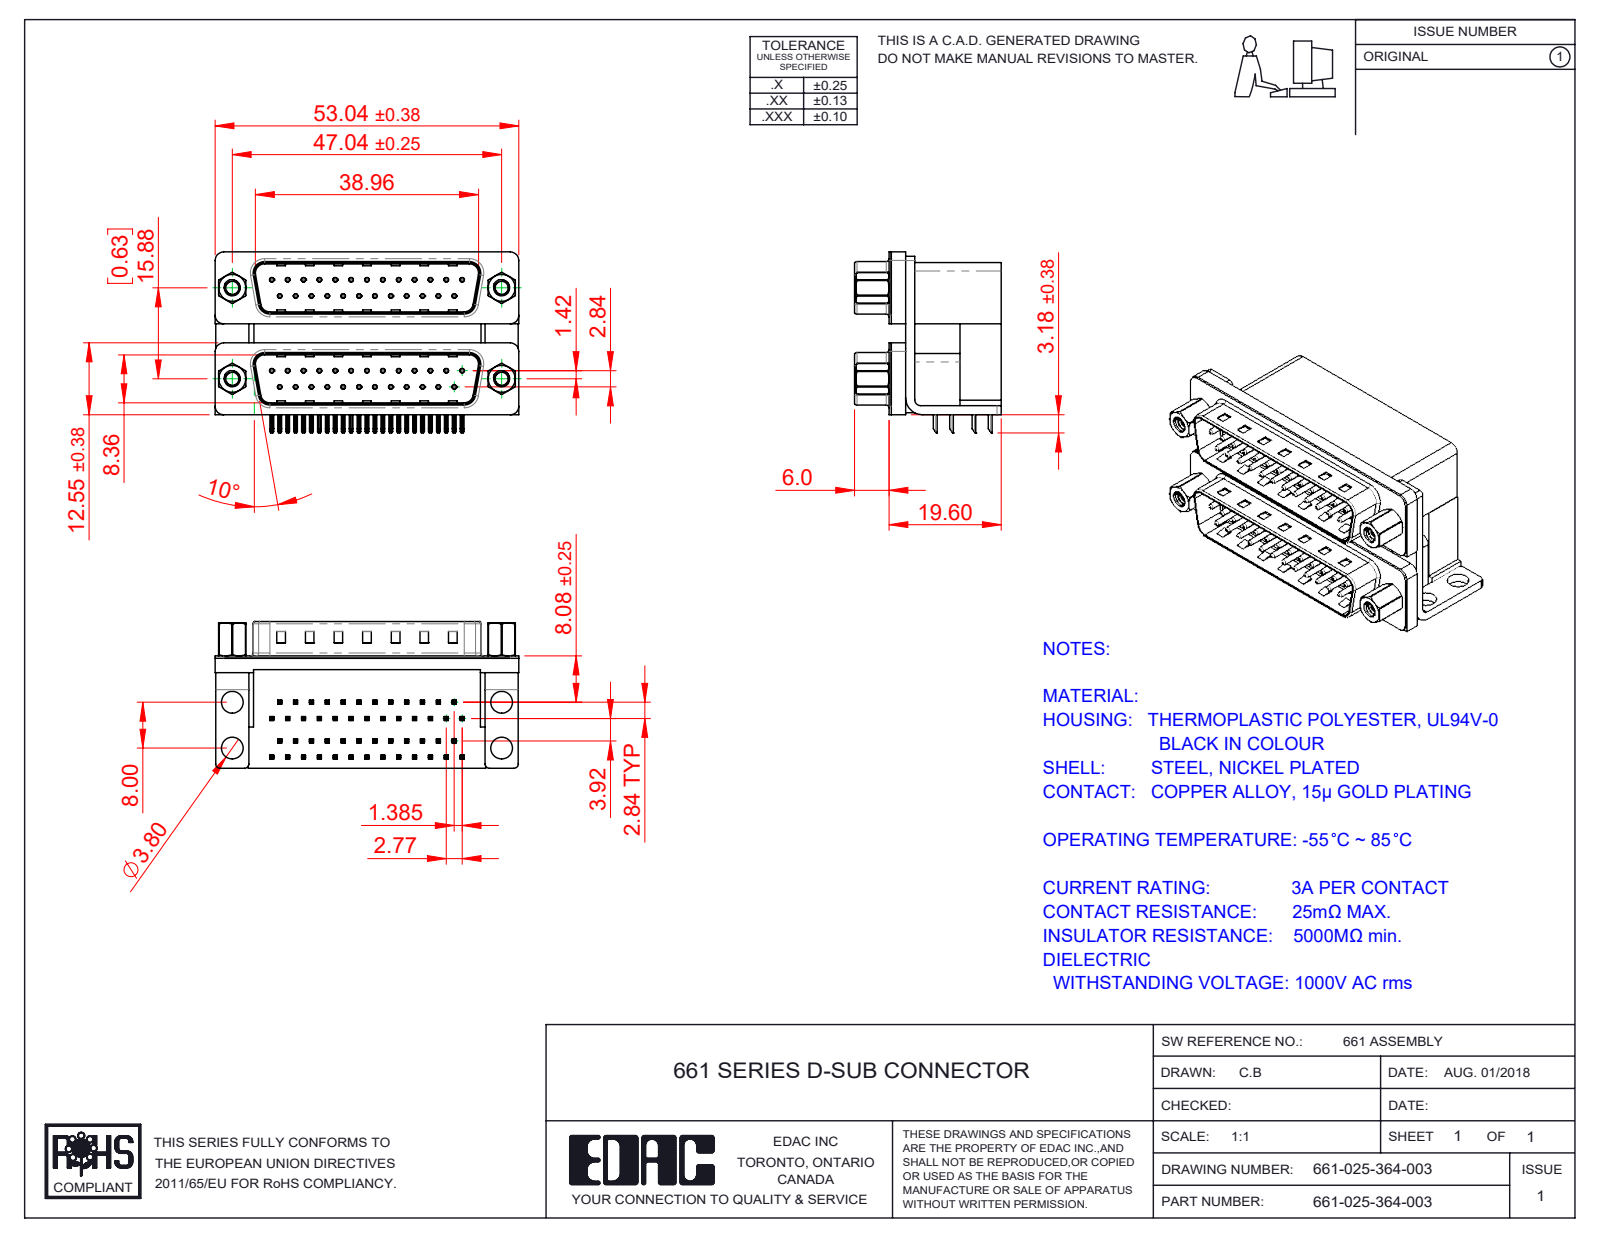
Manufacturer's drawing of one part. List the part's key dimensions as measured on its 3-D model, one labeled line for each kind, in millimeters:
Part name (STEP PRODUCT): 661 Contact Top Upper_L; 661 Contact Bottom Lower; 661 Shell_25 Contacts; 661 Housing Spacer_25 Contacts L (+8 more)
STEP written by: SolidWorks 2020 (CONFIG_CONTROL_DESIGN)
Units: millimetres
Bodies: 65 solids, 4846 faces (2978 planar, 1410 cylindrical, 458 other)
Overall size (bounding box): 53.04 × 31.61 × 25.6
Volume: 20 490 mm³ · Surface area: 21 756 mm²
Round holes (diameter × count): ⌀0.35 ×50, ⌀0.8 ×50, ⌀2.26 ×4, ⌀2.29 ×4, ⌀3.5 ×4, ⌀4 ×4, ⌀4.8 ×4, ⌀5 ×4
Round bosses / shafts (diameter × count): ⌀0.75 ×50, ⌀4.9 ×4, ⌀4.75 ×4, ⌀3.9 ×4, ⌀2.79 ×4
Partial cylindrical surfaces — rounded edges, fillets, slot ends (radius × count): R0.25 ×200, R0.12 ×100, R0.5 ×16, R1.5 ×13, R0.9 ×8, R1.6 ×8, R2 ×8, R0.4 ×4
Main face-to-face distances: 0.4, 19.2, 7.2, 12, 15.87, 10.7, 16.7, 9.5, 2.5, 15.53
Hole centre spacings: 3.16, 2.77, 5.54, 8.31, 11.08, 13.85, 16.62, 5.03
